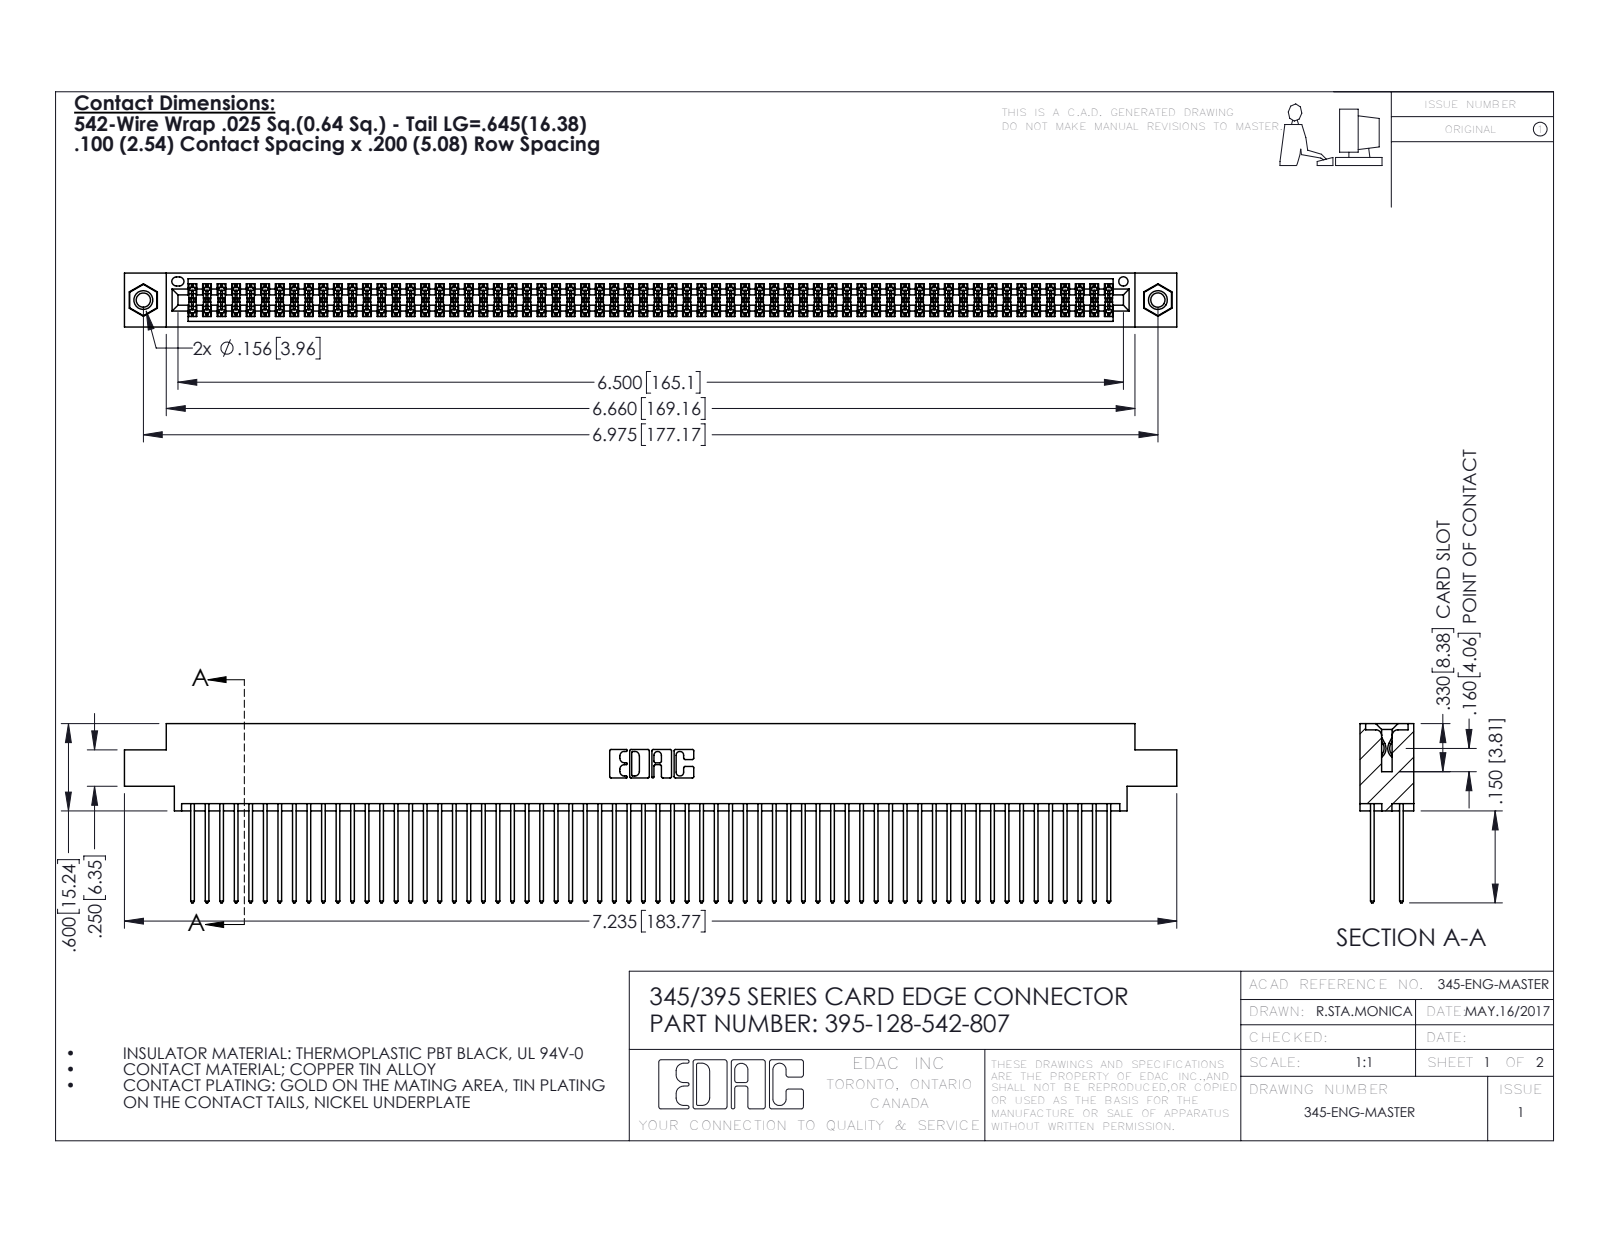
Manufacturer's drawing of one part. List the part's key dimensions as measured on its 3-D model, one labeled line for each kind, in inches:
Part name (STEP PRODUCT): 395-128-542-807; 345-250-001_345-250-005-103; 345-292-001_345-293-142; 345 Part_0.170 Offset - 0.156 Dia-TI
STEP written by: SolidWorks 2016 (CONFIG_CONTROL_DESIGN)
Units: inches
Bodies: 131 solids, 6590 faces (4340 planar, 2234 cylindrical, 16 other)
Overall size (bounding box): 7.235 × 1.232 × 0.37
Volume: 1.13 in³ · Surface area: 47.69 in²
Round holes (diameter × count): ⌀0.098 ×2, ⌀0.125 ×2, ⌀0.156 ×2, ⌀0.064 ×1
Round bosses / shafts (diameter × count): ⌀0.155 ×2
Partial cylindrical surfaces — rounded edges, fillets, slot ends (radius × count): R0.006 ×192, R0.01 ×128, R0.01 ×22, R0.007 ×6, R0.031 ×6, R0.026 ×3, R0.014 ×2, R0.019 ×2
Main face-to-face distances: 0.072, 0.298, 0.2, 0.098, 0.272, 0.025, 0.225, 0.37, 0.175, 0.149
Hole centre spacings: 0.27, 6.739, 6.975
